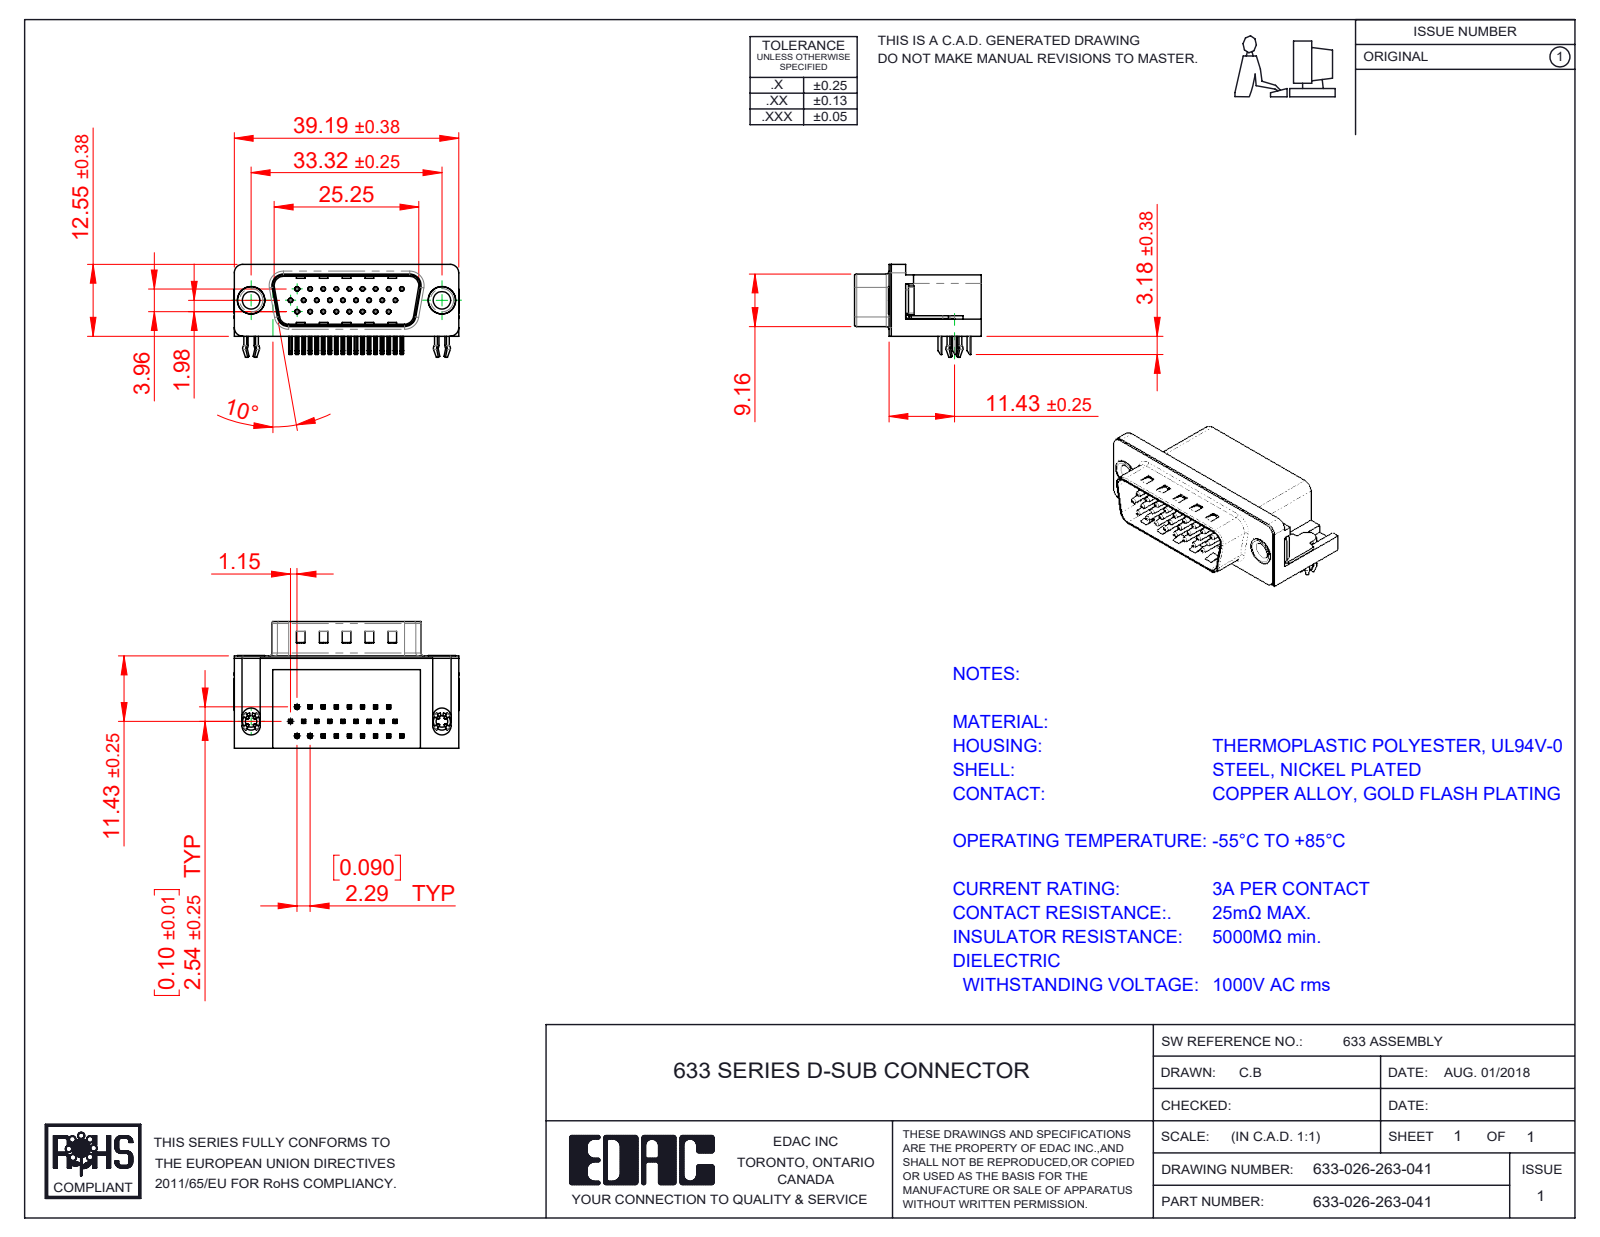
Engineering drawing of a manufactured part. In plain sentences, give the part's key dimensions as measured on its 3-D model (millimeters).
The part is named "633 Contact Middle; 633 Thru Hole Rivet; 633 Shell_26 Contact; 633 4 Prong Board Lock (+4 more)". Its 3-D file was written by "SolidWorks 2016 (CONFIG_CONTROL_DESIGN)". It is 32 solids with 2384 faces: 1463 planar, 666 cylindrical and 255 other. Overall it measures 39.22 by 22.1 by 16.25 millimeters. Its volume is 5 596 cubic millimeters and its surface area 7 305 square millimeters. Round holes: 26 of diameter 0.35, 26 of diameter 0.8, 2 of diameter 2, 2 of diameter 3.05, 2 of diameter 4, 2 of diameter 4.8, 2 of diameter 5. Round bosses or shafts: 26 of diameter 0.75, 2 of diameter 4.9, 2 of diameter 4.75, 2 of diameter 3.85, 2 of diameter 3. Partial cylindrical surfaces (rounded edges, fillets, slot ends): 116 of radius 0.25, 52 of radius 0.12, 16 of radius 1, 9 of radius 0.5, 8 of radius 1.5, 8 of radius 1.6, 4 of radius 0.9, 4 of radius 2. The main face-to-face distances are 0.4, 10.35, 15.7, 2.9, 2.5, 16.1, 8.76, 0.35, 10.7, 0.5. The hole center spacings are 2.29, 4.57, 2.28, 3.96, 6.05, 4.58, 6.86, 7.92.
